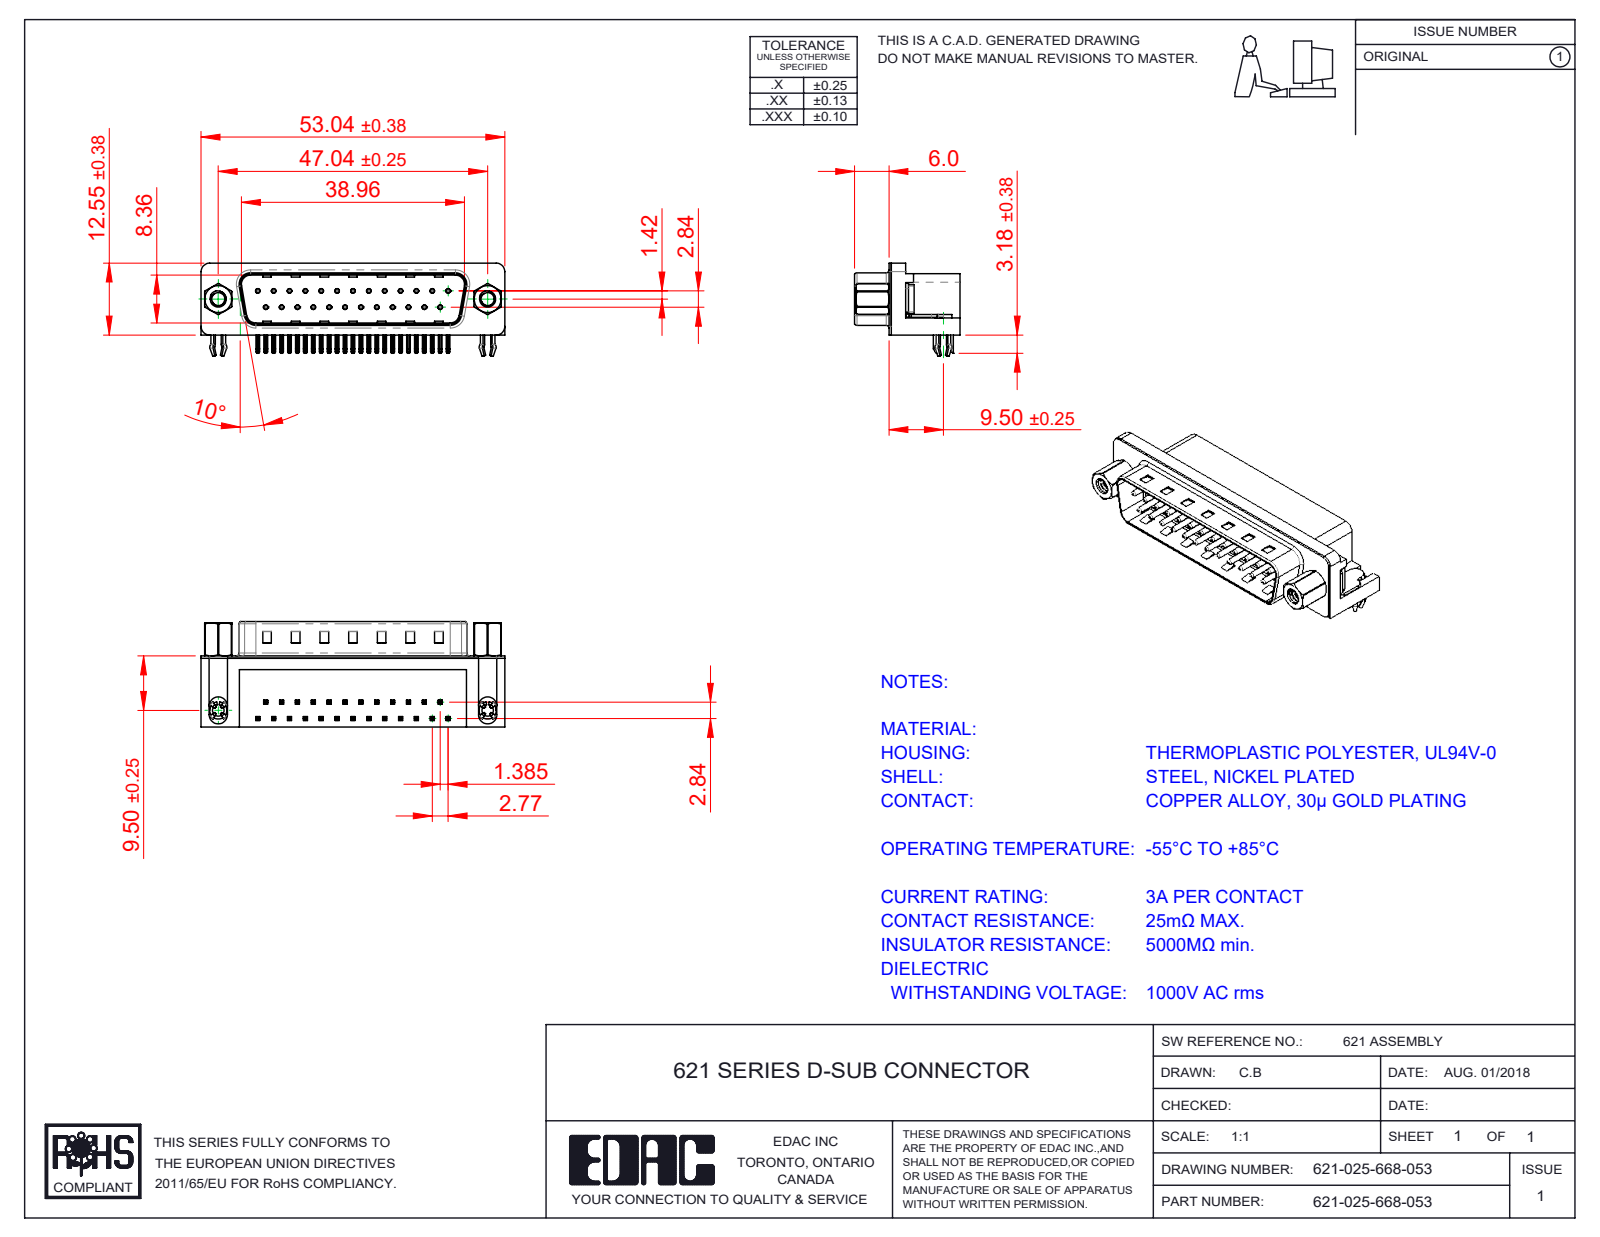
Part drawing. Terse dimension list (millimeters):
name: 621 4-40 Hex Standoff 5; 621 Contact Bottom; 621 Housing_25 Socket; 621 4-40 Threaded Board Mount (+4 more)
written by: SolidWorks 2016 (CONFIG_CONTROL_DESIGN)
unit: mm
bodies: 33 solids, 2419 faces (1427 planar, 743 cylindrical, 249 other)
size: 53.04 × 18.4 × 15.73
volume: 6 572 mm³; area: 8 245 mm²
holes: 25× ⌀0.35, 25× ⌀0.8, 4× ⌀2.26, 2× ⌀2.29, 2× ⌀4, 2× ⌀4.8, 2× ⌀5
bosses: 25× ⌀0.75, 2× ⌀4.9, 2× ⌀4.75, 2× ⌀3.9, 2× ⌀3.26, 2× ⌀2.79
rounds: 108× R0.25, 50× R0.12, 16× R1, 9× R0.5, 8× R1.6, 7× R1.5, 4× R0.9, 4× R2
face distances: 0.4, 12, 10.35, 2.1, 8.76, 10.46, 1.7, 10.86, 12.4, 9
hole spacings: 3.16, 2.77, 5.54, 8.31, 11.08, 13.85, 16.62, 5.03
